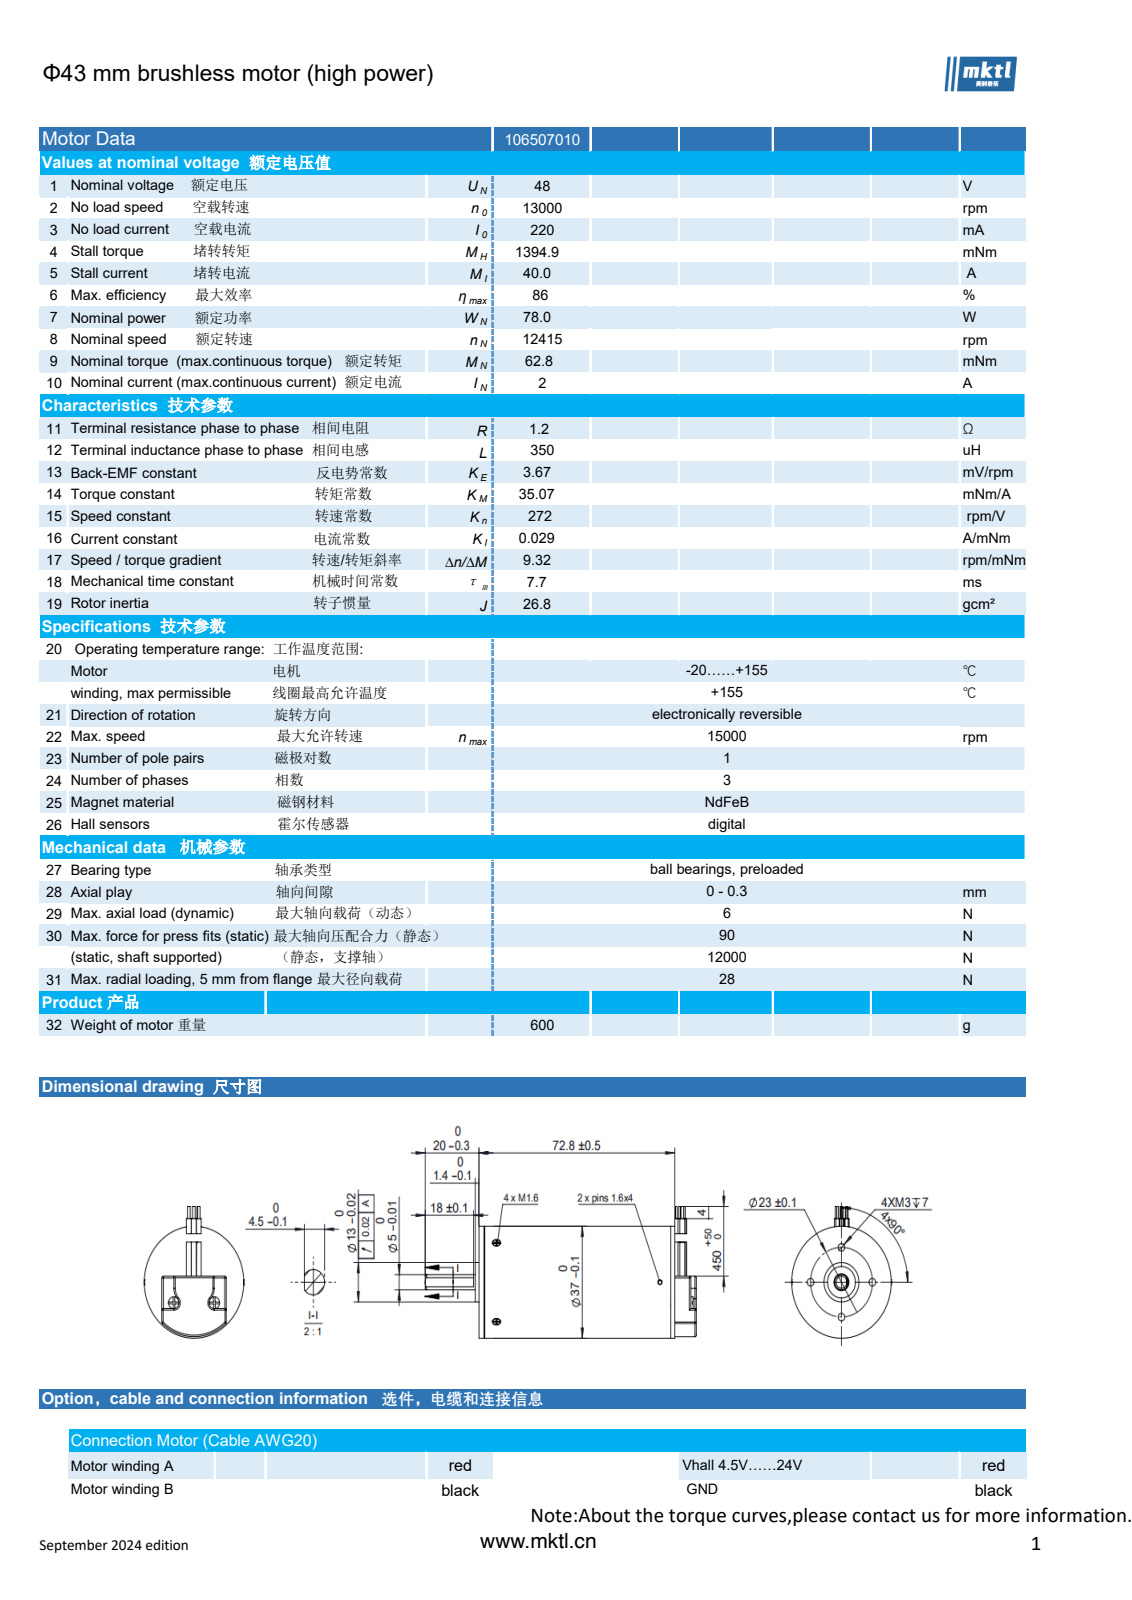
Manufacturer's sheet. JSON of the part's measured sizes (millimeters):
{"part_name": "approval 106507010", "step_written_by": "SolidWorks 2018 (CONFIG_CONTROL_DESIGN)", "units": "millimeters", "bodies": {"solids": 346, "faces": 3585, "planar": 1420, "cylindrical": 1860, "other": 305}, "overall_size": [100.8, 43.5, 37], "volume_mm3": 75388, "surface_area_mm2": 270800, "round_holes": [[2.1, 6], [0.75, 5], [1, 4], [2.5, 4], [1.5, 3], [1.6, 3], [3, 3], [1.2, 2], [1.65, 2], [2.05, 2], [3.1, 2], [1.3, 1]], "round_bosses_or_shafts": [[1.2, 16], [1.8, 12], [0.5, 12], [0.58, 6], [4, 5], [1.6, 5], [0.6, 5], [1, 3]], "partial_cylinders_radius": [[0.1, 24], [0.5, 18], [0.75, 11], [1, 10], [0.42, 8], [0.6, 7], [0.3, 3], [1.9, 2]], "face_to_face_distances": [0.4, 0.6, 1, 0.8, 1.2, 1.4, 1.6, 1.8, 2, 15], "hole_center_spacings": [2, 2.3, 11.5, 13.25, 16.26, 18.78, 23, 23.79]}
